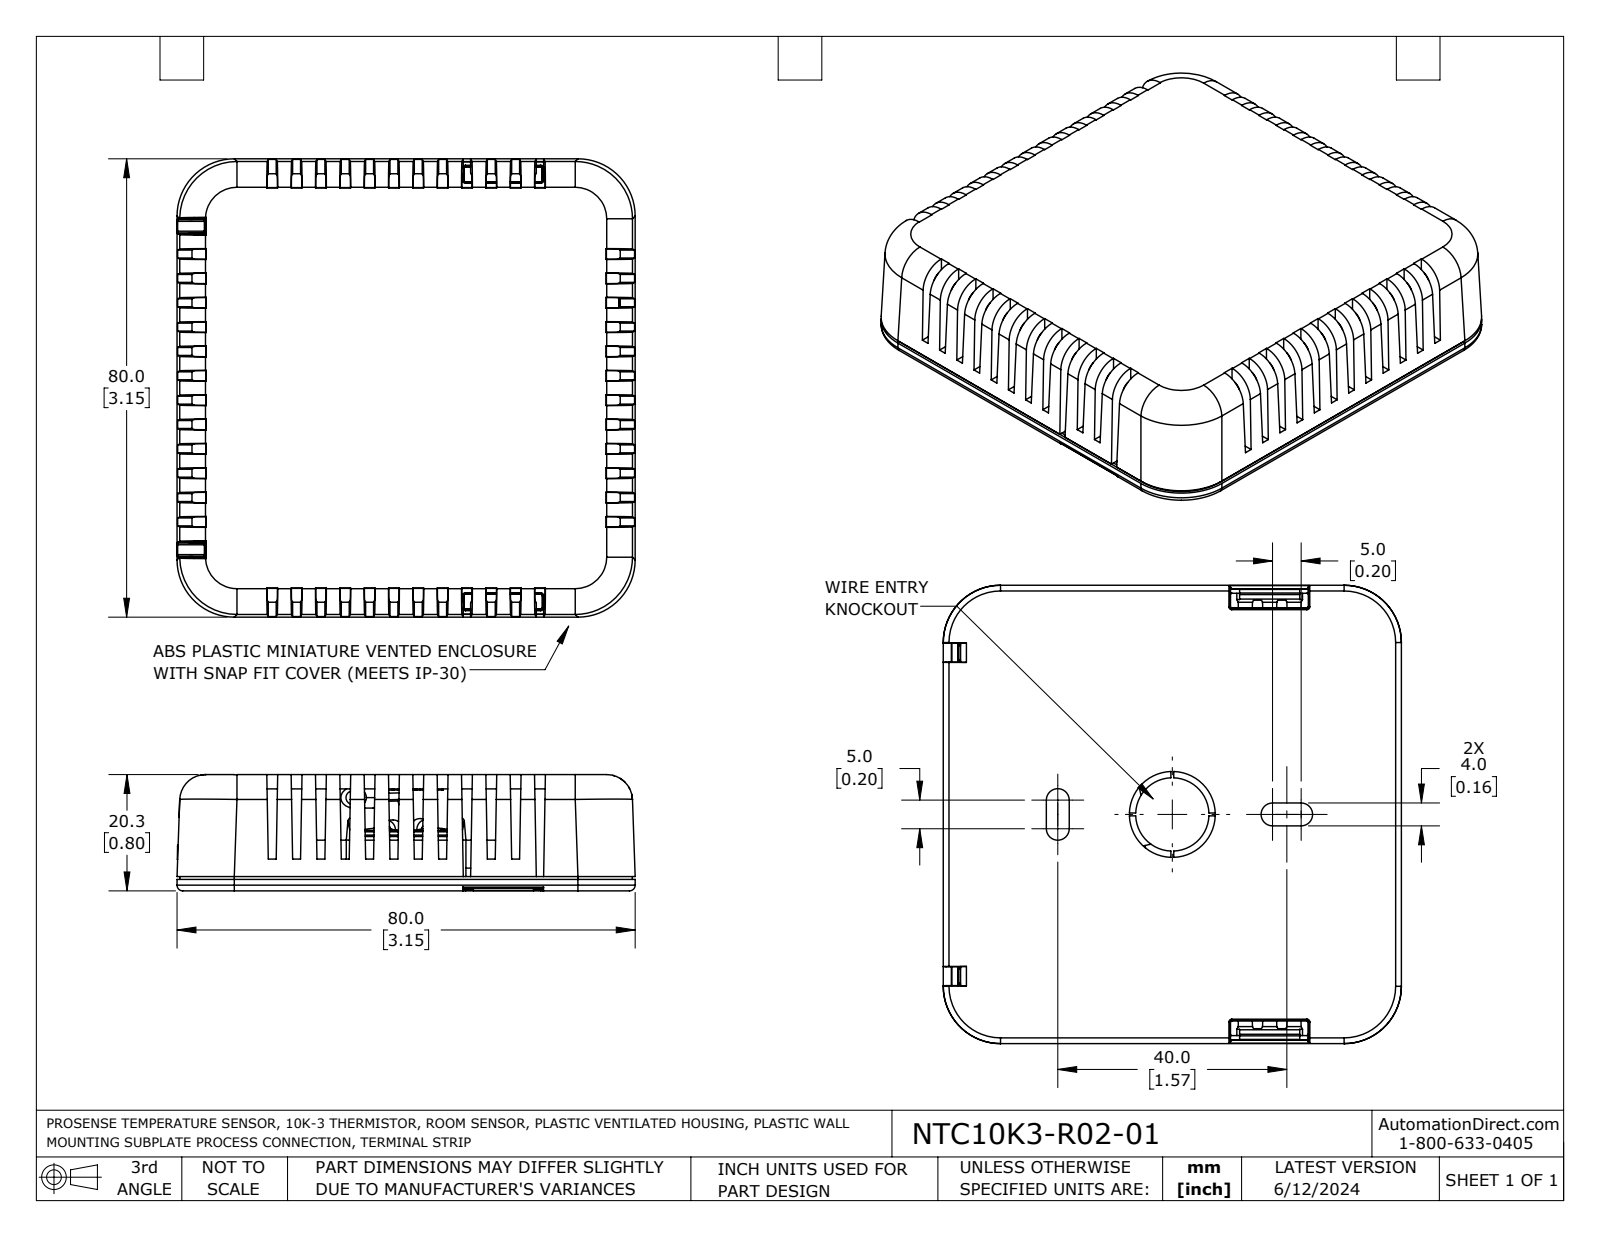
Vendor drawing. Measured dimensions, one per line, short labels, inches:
name: NTC10K3-R02-01
written by: SolidWorks 2021 (AUTOMOTIVE_DESIGN)
unit: in
bodies: 15 solids, 1372 faces (792 planar, 313 cylindrical, 267 other)
size: 3.15 × 3.15 × 0.799
volume: 2.542 in³; area: 66.18 in²
holes: 8× ⌀0.217, 6× ⌀0.175, 4× ⌀0.098, 2× ⌀0.07, 2× ⌀0.146, 2× ⌀0.175
bosses: 4× ⌀0.27, 4× ⌀0.17, 4× ⌀0.12, 2× ⌀0.138, 2× ⌀0.045, 2× ⌀0.045, 2× ⌀0.01
rounds: 24× R0.01, 16× R0.012, 9× R0.037, 9× R0.038, 8× R0.145, 8× R0.394, 6× R0.03, 5× R0.039
face distances: 0.098, 0.701, 0.799, 0.602, 0.167, 0.335, 0.502, 0.669, 0.837, 1.004
hole spacings: 0.3, 0.374, 0.479, 0.748, 0.806, 0.374, 0.48, 1.121
